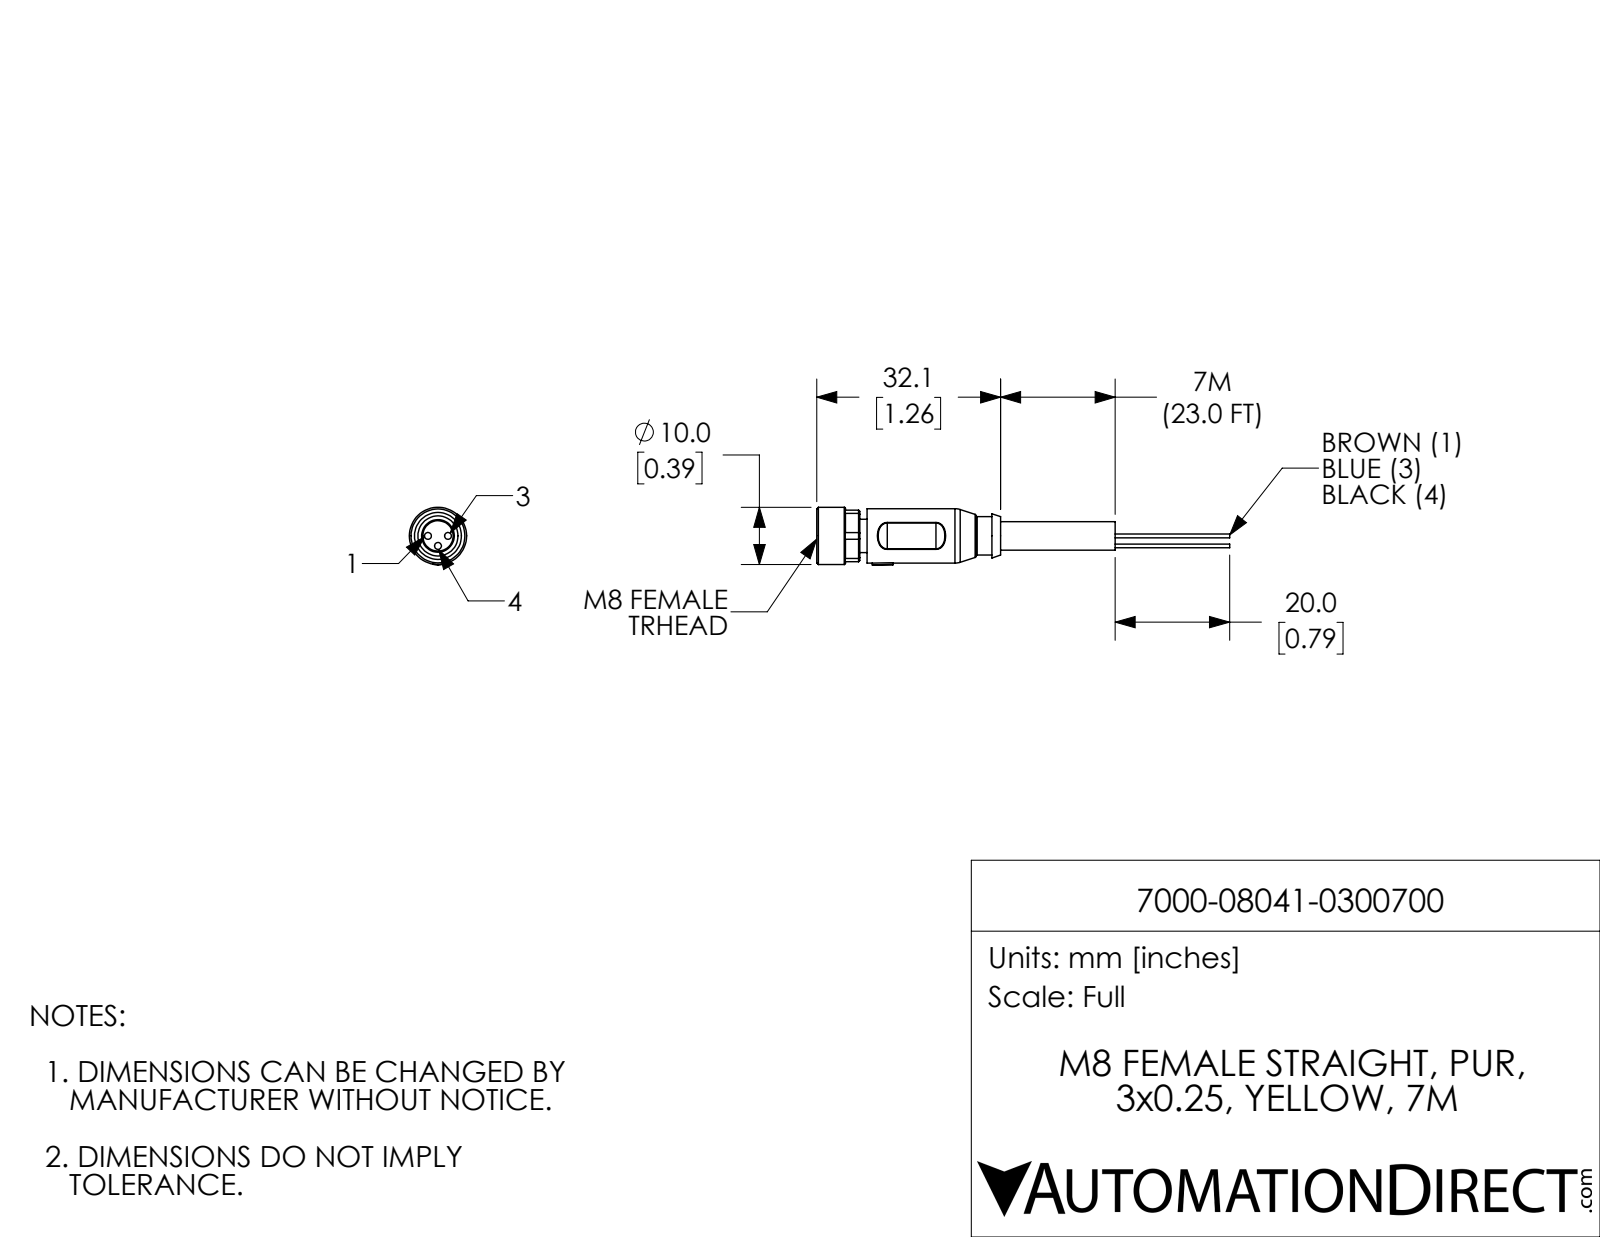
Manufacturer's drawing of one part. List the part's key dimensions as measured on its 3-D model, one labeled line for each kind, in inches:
Part name (STEP PRODUCT): 7000-08041-0300700
STEP written by: SolidWorks 2021 (CONFIG_CONTROL_DESIGN)
Units: inches
Bodies: 1 solid, 109 faces (36 planar, 42 cylindrical, 31 other)
Overall size (bounding box): 2.839 × 0.396 × 0.394
Volume: 0.141 in³ · Surface area: 2.851 in²
Round holes (diameter × count): ⌀0.047 ×3, ⌀0.276 ×1
Round bosses / shafts (diameter × count): ⌀0.026 ×3, ⌀0.394 ×1, ⌀0.374 ×1, ⌀0.264 ×1, ⌀0.228 ×1, ⌀0.224 ×1, ⌀0.197 ×1
Partial cylindrical surfaces — rounded edges, fillets, slot ends (radius × count): R0.008 ×4, R0.098 ×4, R0.193 ×1, R0.199 ×1
Main face-to-face distances: 0.327, 0.051, 0.969, 0.354, 0.059, 0.028, 0.268, 0.319, 2.024, 1.756
Hole centre spacings: 0.069, 0.097, 0.138
